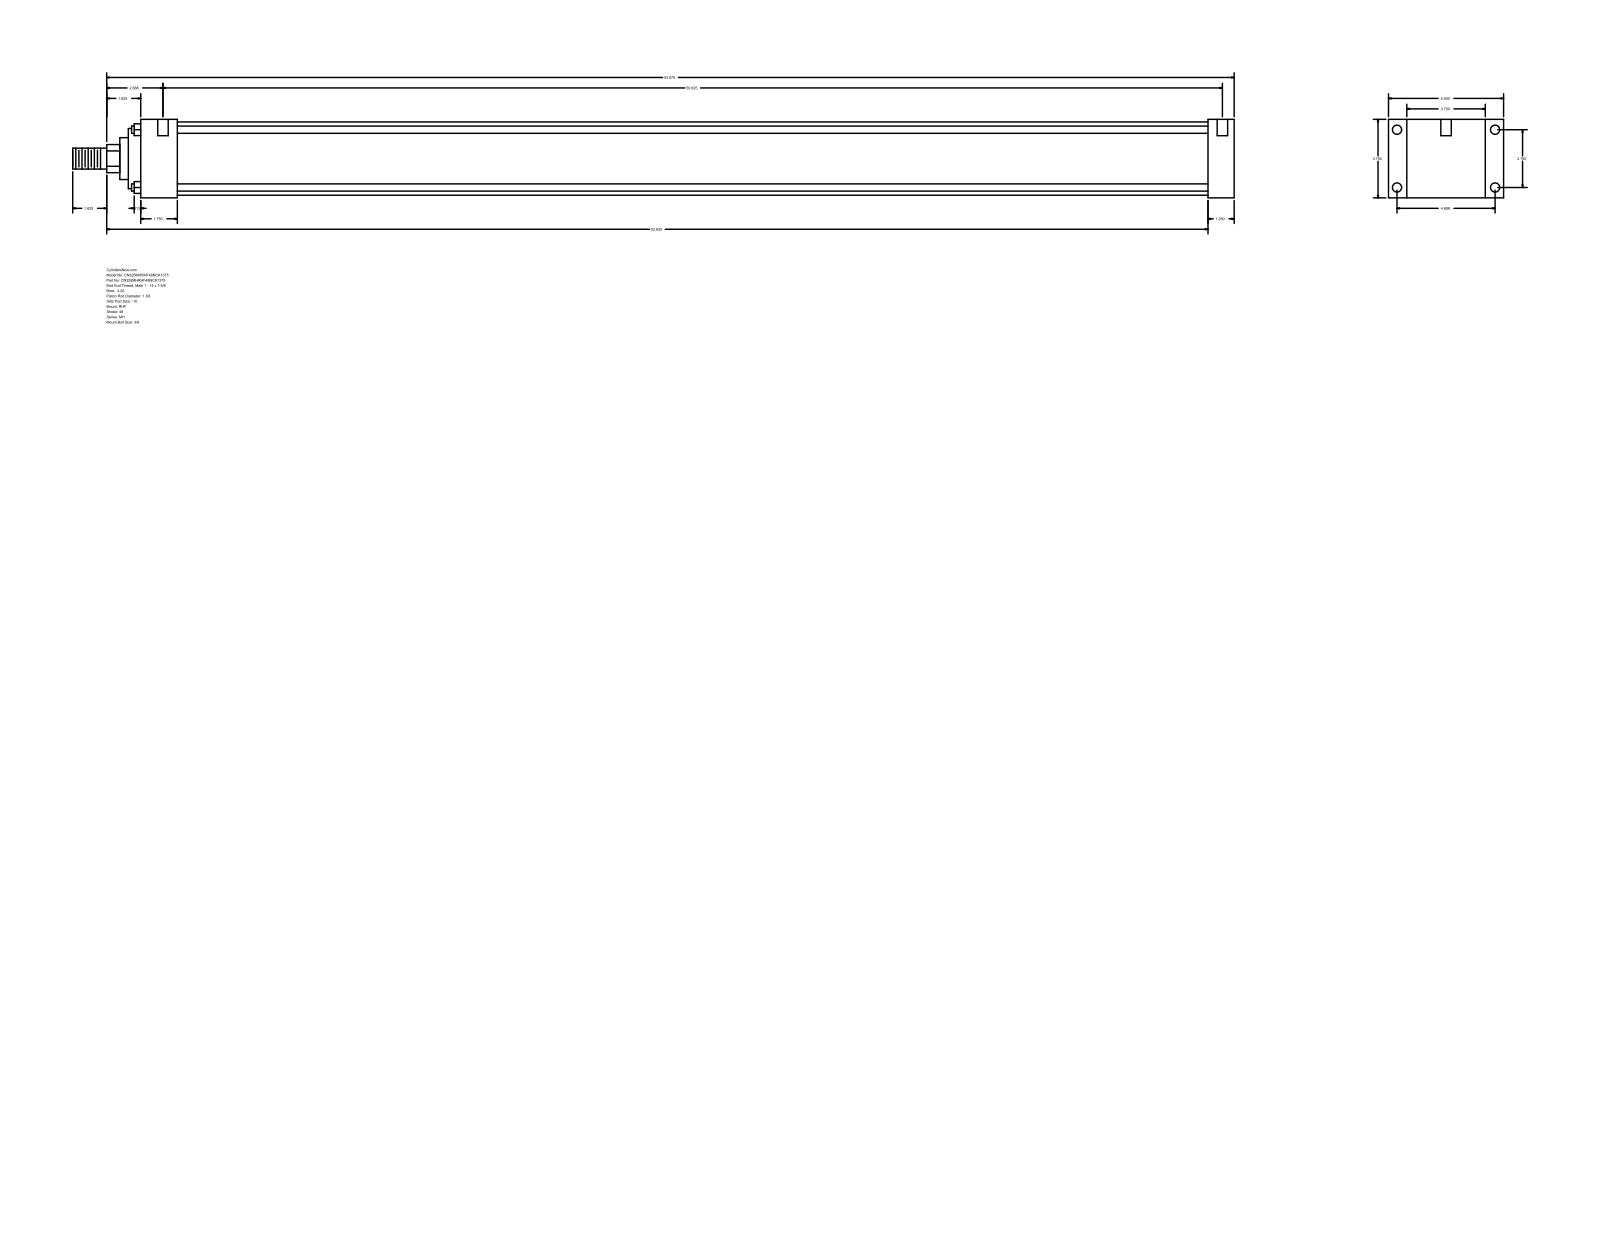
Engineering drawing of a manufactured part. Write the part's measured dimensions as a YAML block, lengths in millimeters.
part_name: "MH_RHF__0325_1.375"
step_written_by: "GSSL Pune (CONFIG_CONTROL_DESIGN)"
units: millimeters
bodies: {solids: 0, faces: 90, planar: 61, cylindrical: 29, other: 0}
overall_size: [1409.7, 139.7, 95.25]
round_holes:
  - {diameter: 5.56, count: 4}
  - {diameter: 11.13, count: 4}
  - {diameter: 12.7, count: 2}
round_bosses_or_shafts:
  - {diameter: 8.76, count: 4}
  - {diameter: 88.9, count: 1}
  - {diameter: 73.03, count: 1}
  - {diameter: 50.8, count: 1}
  - {diameter: 34.92, count: 1}
  - {diameter: 25.4, count: 1}
partial_cylinders:
  - {radius: 17.06, count: 1}
face_to_face_distances: [95.24, 31.75, 22.23, 117.47, 1295.4, 1327.15, 139.7, 44.45, 1250.95, 1282.7]
hole_center_spacings: [70.1, 119.06, 138.16, 1292.23, 1.59, 4.76, 1285.88, 1287.47]
